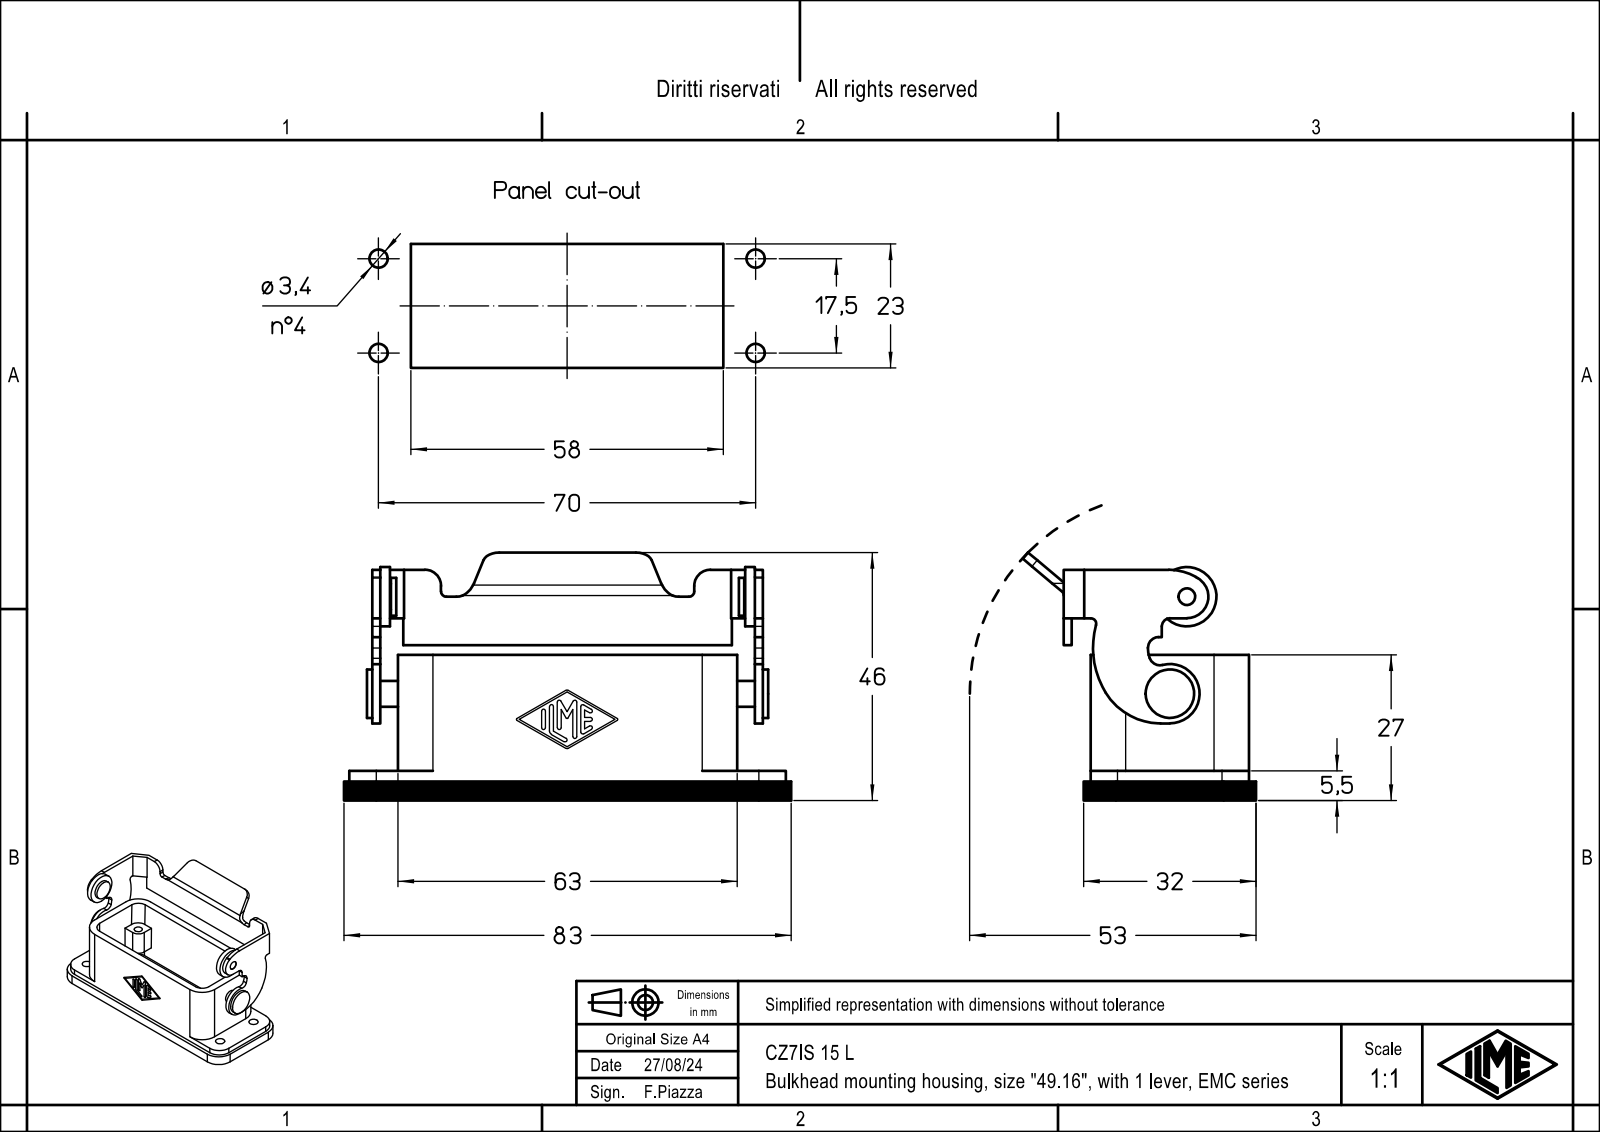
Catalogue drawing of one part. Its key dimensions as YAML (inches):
part_name: "CZ7IS 15 L"
step_written_by: "Creo Elements/Direct Modeling 20.5B 27-May-2023 (C) Parametric Technology GmbH (AUTOMOTIVE_DESIGN)"
units: inches
bodies: {solids: 1, faces: 210, planar: 100, cylindrical: 110, other: 0}
overall_size: [3.268, 1.811, 1.704]
volume: 1.311
surface_area: 27.85
round_holes:
  - {diameter: 0.118, count: 4}
  - {diameter: 0.134, count: 4}
  - {diameter: 0.122, count: 1}
  - {diameter: 0.197, count: 1}
round_bosses_or_shafts:
  - {diameter: 0.189, count: 2}
  - {diameter: 0.433, count: 1}
  - {diameter: 0.354, count: 1}
  - {diameter: 0.276, count: 1}
  - {diameter: 0.118, count: 1}
partial_cylinders:
  - {radius: 0.118, count: 10}
  - {radius: 0.098, count: 5}
  - {radius: 0.039, count: 4}
  - {radius: 0.138, count: 4}
  - {radius: 0.197, count: 4}
  - {radius: 0.236, count: 4}
  - {radius: 0.256, count: 4}
  - {radius: 0.079, count: 2}
face_to_face_distances: [0.109, 1.049, 0.059, 1.157, 0.94, 0.138, 2.795, 0.128, 0.187, 2.667]
hole_center_spacings: [0.405, 0.773, 2.352, 2.443, 0.63, 0.689, 1.949, 2.048]
